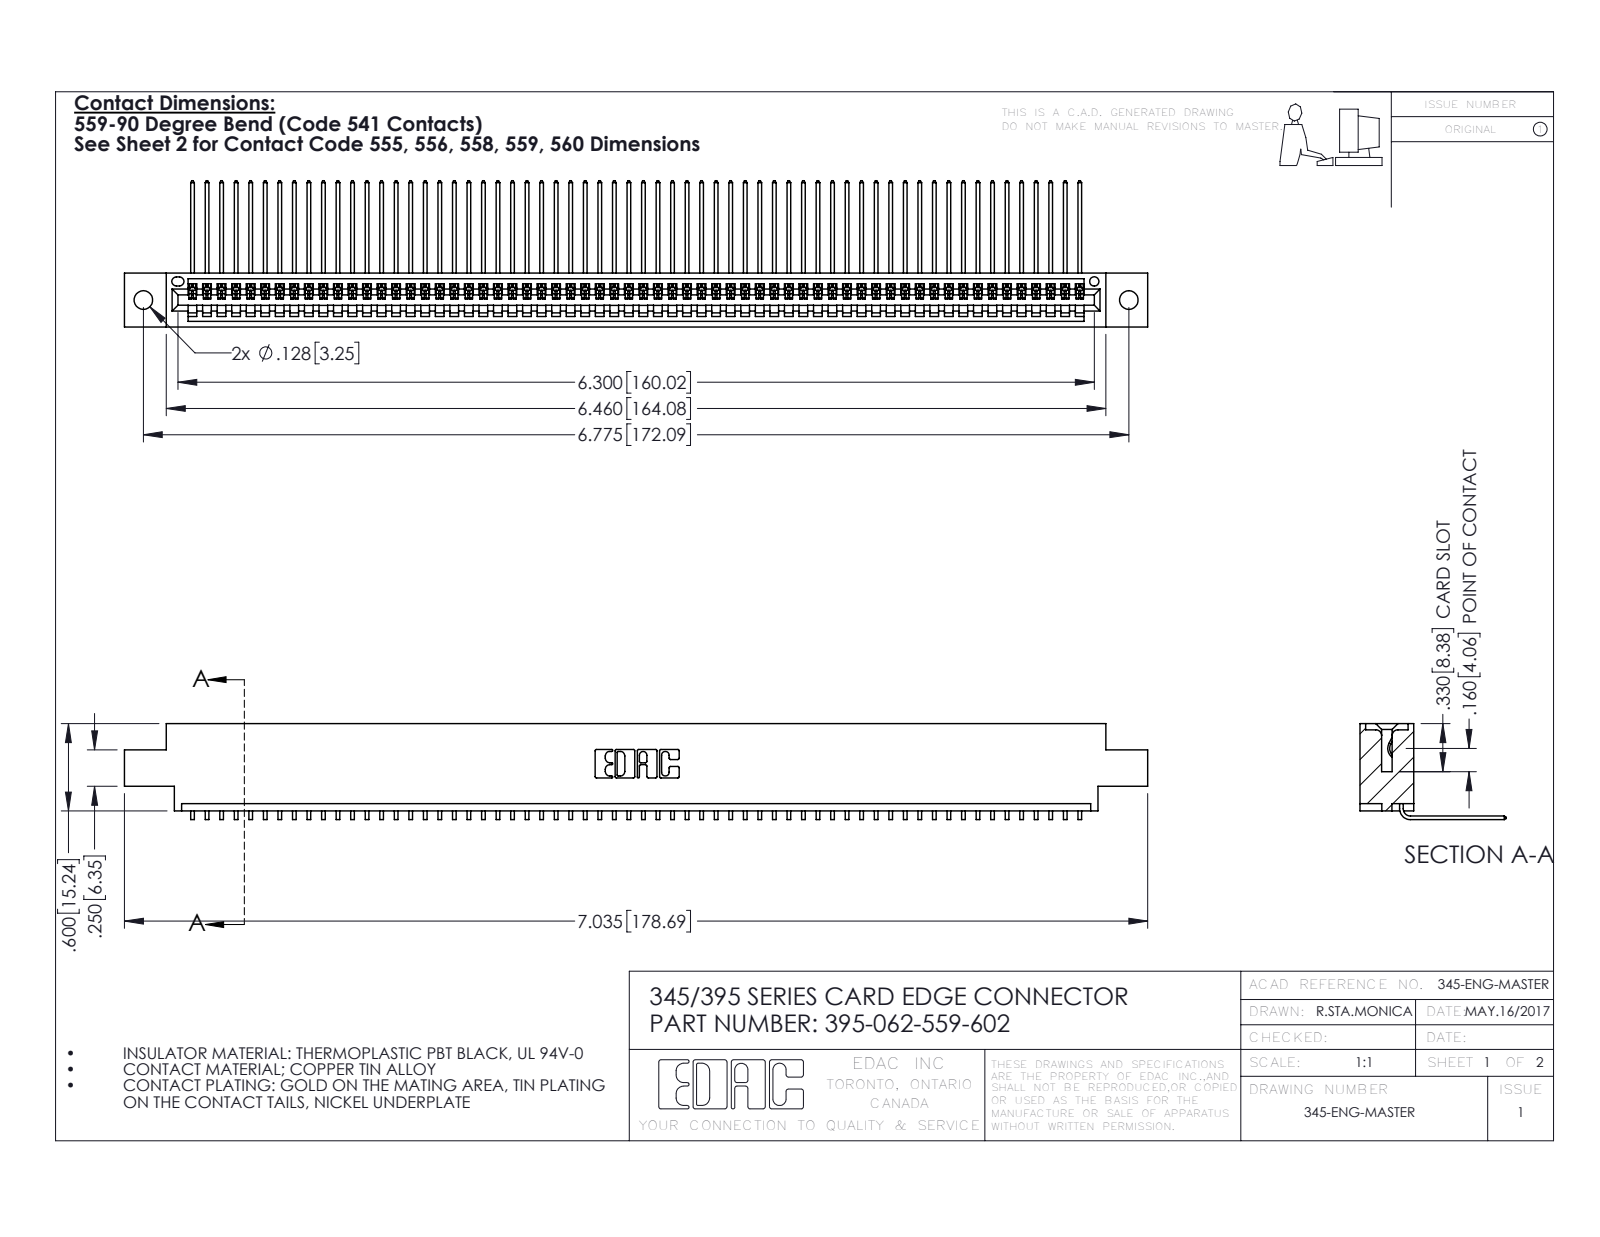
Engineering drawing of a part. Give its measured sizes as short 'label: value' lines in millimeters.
name: 395-062-559-602; 345 Part_0.170 Offset - 0.128 Dia; 345-292-001_558 559 Tail - 1
written by: SolidWorks 2016 (CONFIG_CONTROL_DESIGN)
unit: mm
bodies: 63 solids, 3850 faces (2688 planar, 1162 cylindrical, 0 other)
size: 178.7 × 25.5 × 16.7
volume: 17 190 mm³; area: 24 190 mm²
holes: 2× ⌀3.3, 1× ⌀1.6
rounds: 124× R0.2, 22× R0.3, 6× R0.2, 6× R0.8, 3× R0.7, 2× R0.8, 2× R1, 1× R0.4
face distances: 1.8, 7.6, 9.4, 5.1, 2.5, 6.9, 0.6, 5.7, 4.4, 3.8
hole spacings: 6.9, 166.1, 172.1
